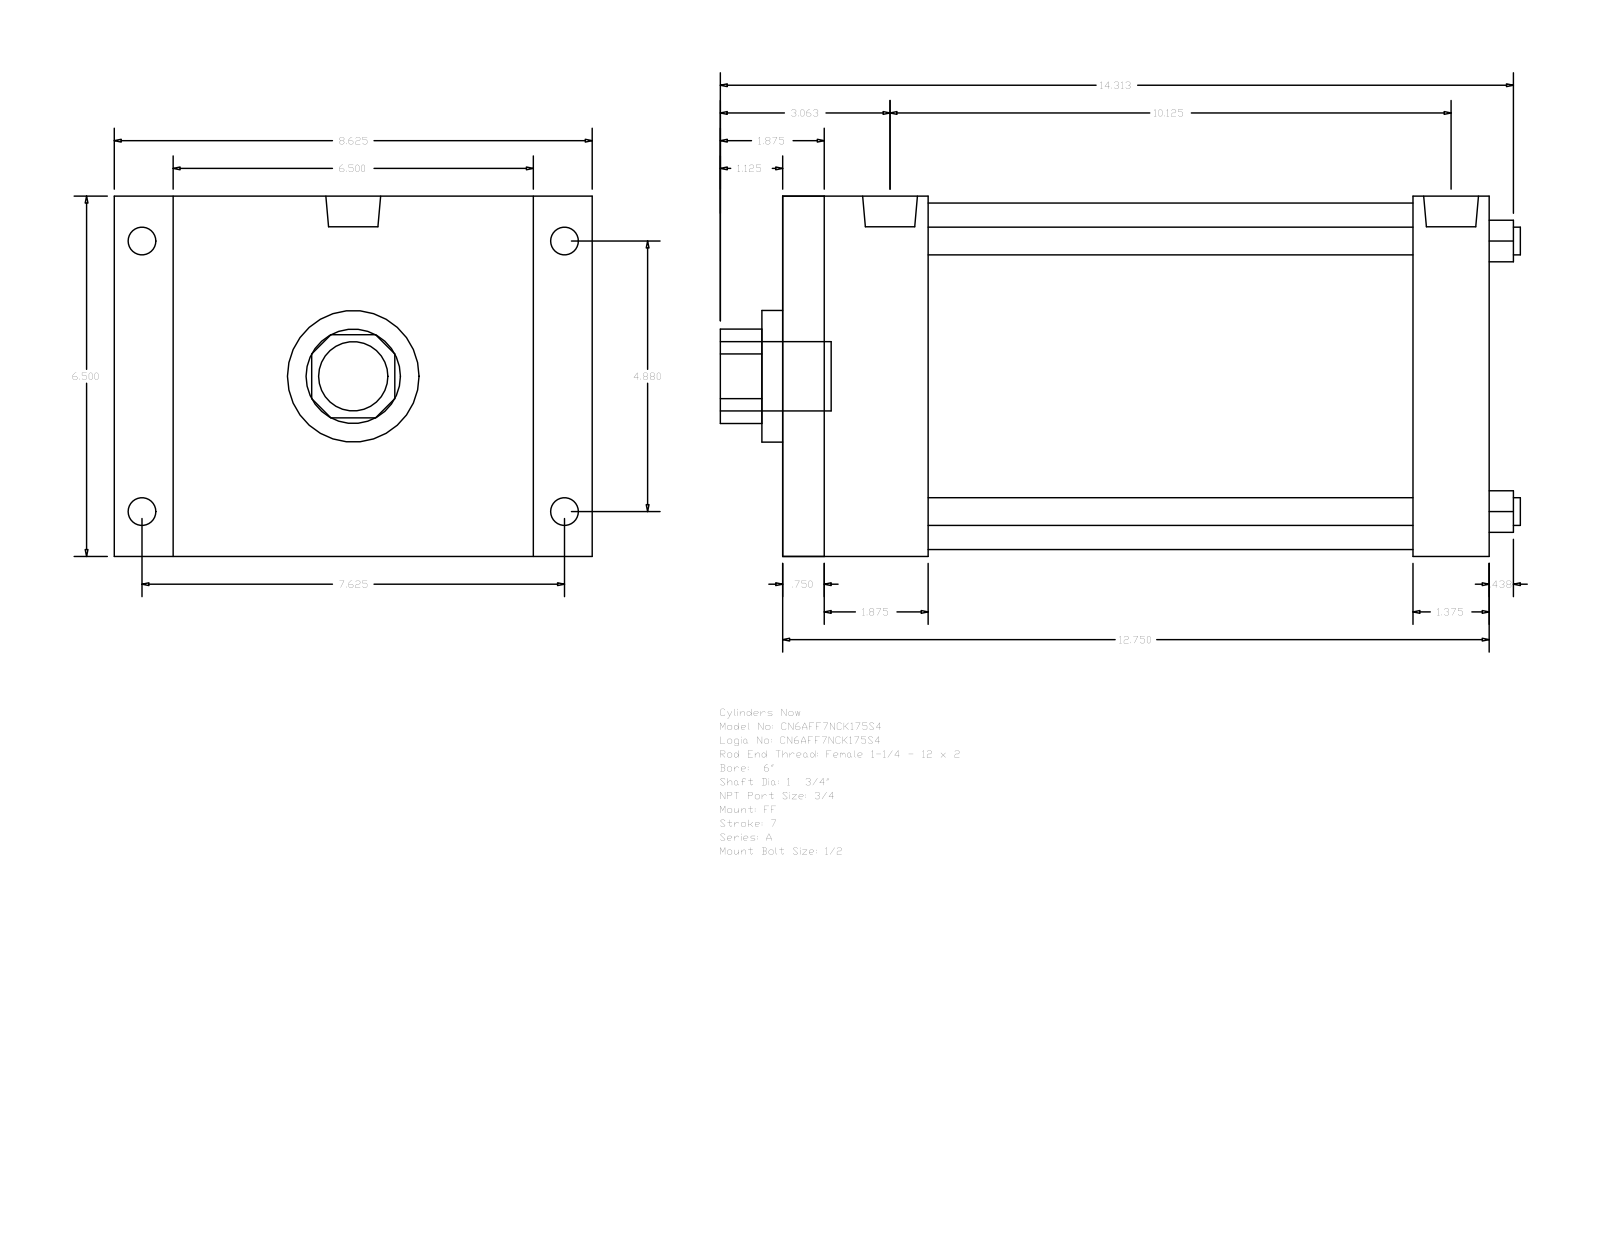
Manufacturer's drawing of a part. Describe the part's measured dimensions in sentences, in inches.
The part is named "A_FF__0600_1.75". Its 3-D file was written by "GSSL Pune (CONFIG_CONTROL_DESIGN)". It is 0 solids with 92 faces: 64 planar, 28 cylindrical and 0 other. Overall it measures 14.437 by 8.625 by 6.5 inches. Round holes: 4 of diameter 0.5, 1 of diameter 1.75, 1 of diameter 2.375, 1 of diameter 6.25. Round bosses or shafts: 4 of diameter 0.594, 4 of diameter 0.5, 2 of diameter 0.989, 1 of diameter 1.25. Partial cylindrical surfaces (rounded edges, fillets, slot ends): 1 of radius 0.852. The main face-to-face distances are 6.5, 12.75, 0.75, 12, 2.625, 1.875, 10.125, 11.375, 10.625, 8.75. The hole center spacings are 3.451, 4.88, 6.902.
